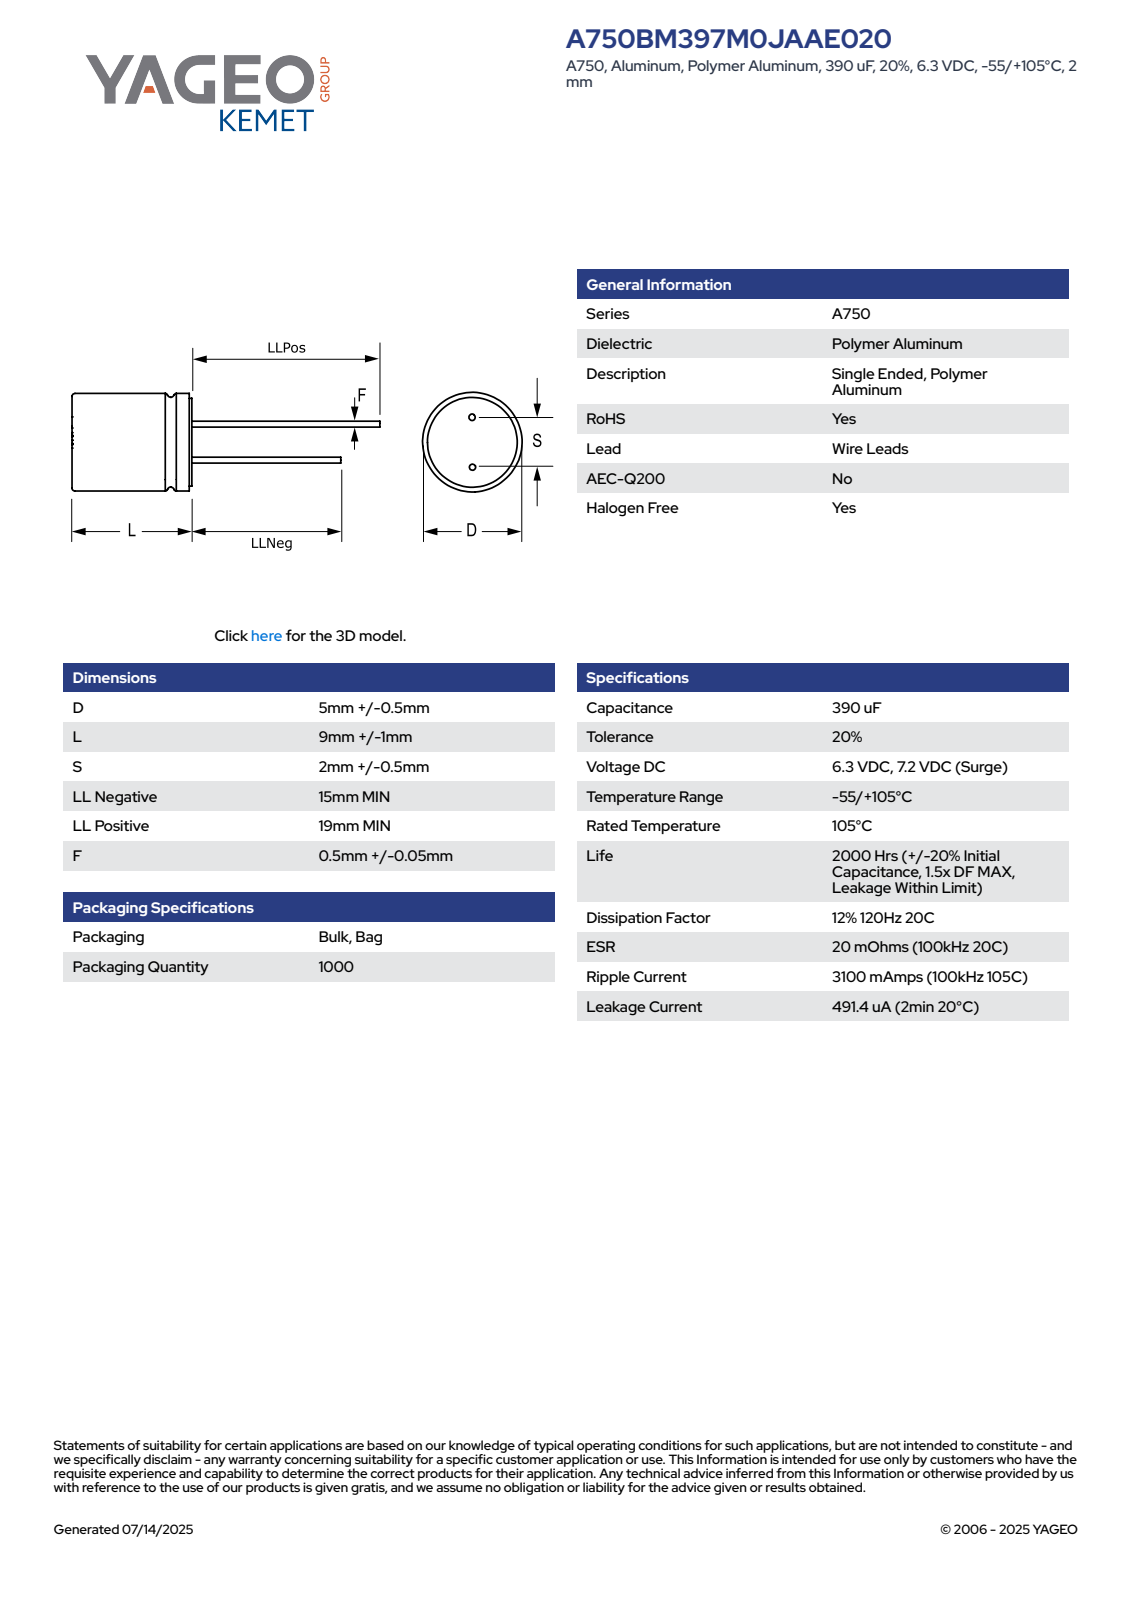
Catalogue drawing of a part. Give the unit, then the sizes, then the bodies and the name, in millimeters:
Units: millimetres
Overall size (bounding box): 29 × 5.5 × 5.5
Round bosses / shafts (diameter × count): ⌀0.55 ×2, ⌀5.5 ×1
Main face-to-face distances: 10, 10.01, 25.01, 29.01, 25, 29, 15, 19, 4, 0.6
Volume: 243 mm³ · Surface area: 285 mm²
Bodies: 4 solids, 75 faces (61 planar, 8 cylindrical, 6 other)
Part name (STEP PRODUCT): CAR_KP_5X9_D5.5L10S2F0.55
STEP written by: SolidWorks 2014 (AUTOMOTIVE_DESIGN)
